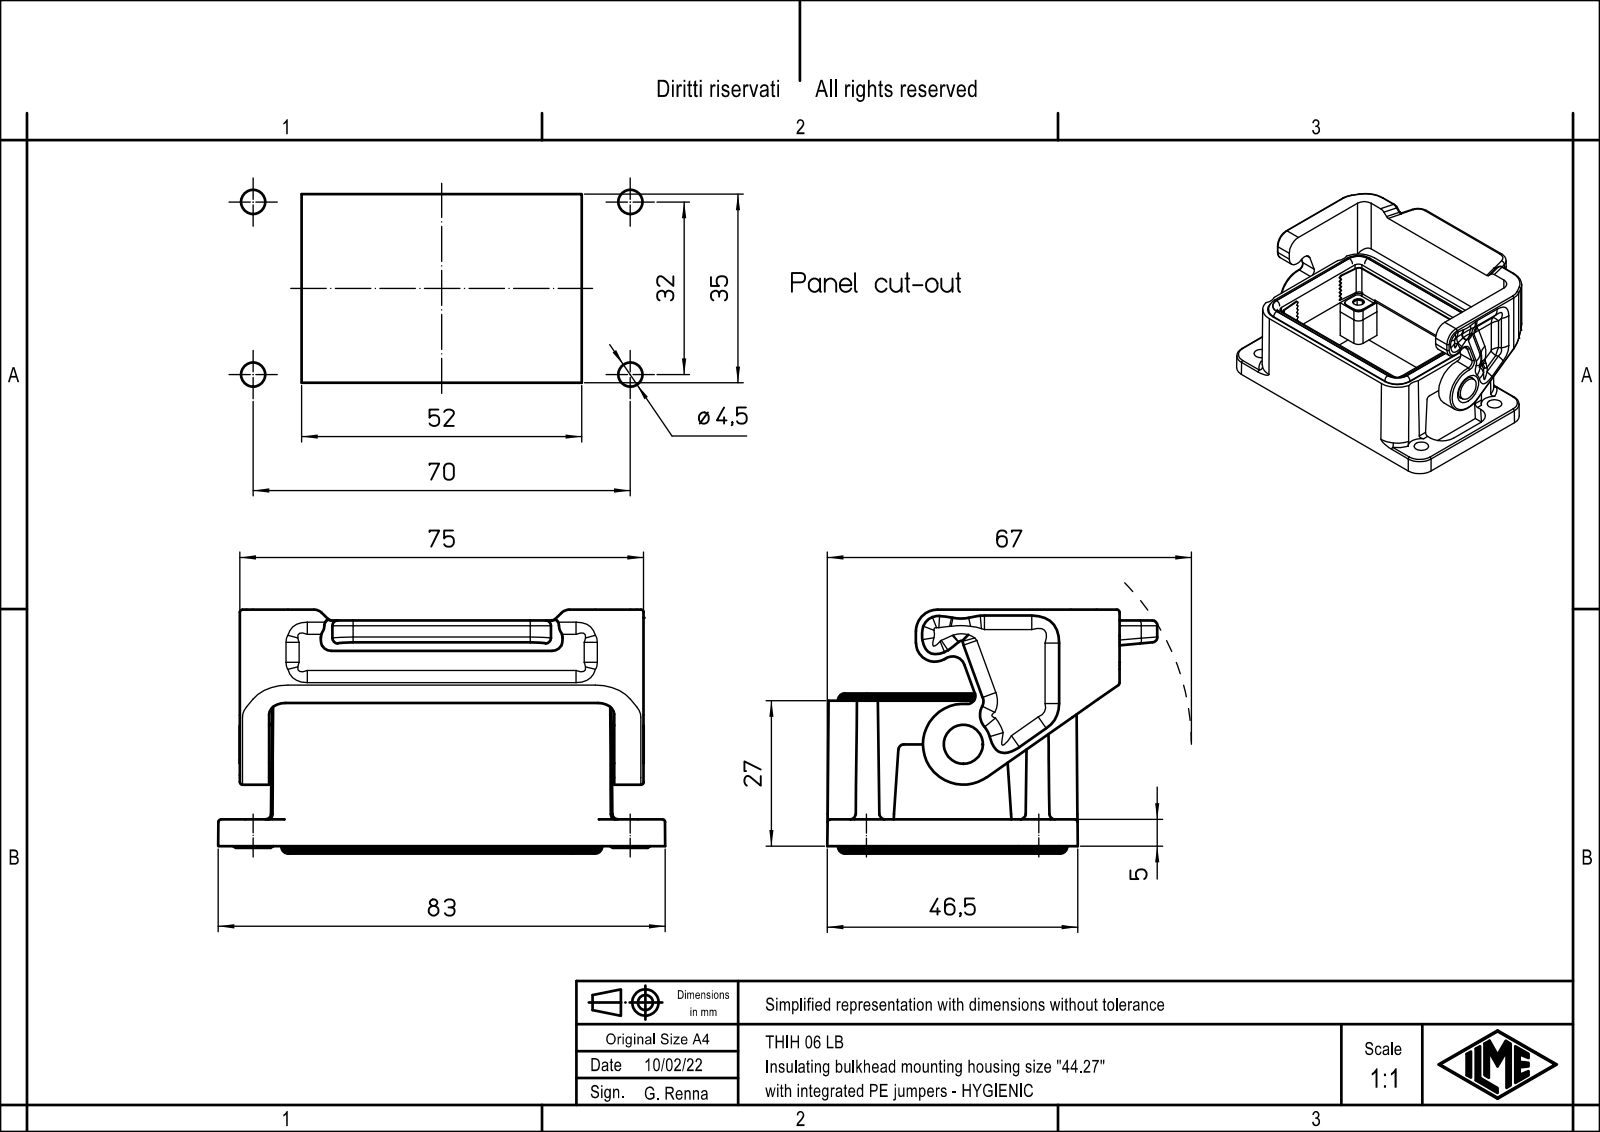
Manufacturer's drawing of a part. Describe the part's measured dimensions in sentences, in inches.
The part is named "53620_D; THIH_06_L". Its 3-D file was written by "Creo Elements/Direct Modeling 20.1B 02-Apr-2019 (C) Parametric Technology GmbH (AUTOMOTIVE_DESIGN)". It is 1 solid with 819 faces: 406 planar, 233 cylindrical and 180 other. Overall it measures 3.268 by 2.411 by 1.781 inches. Its volume is 2.952 cubic inches and its surface area 50.92 square inches. Round holes: 4 of diameter 0.098, 4 of diameter 0.138, 4 of diameter 0.177, 4 of diameter 0.272. Round bosses or shafts: 4 of diameter 0.189, 1 of diameter 0.276. Partial cylindrical surfaces (rounded edges, fillets, slot ends): 36 of radius 0.051, 24 of radius 0.039, 19 of radius 0.059, 15 of radius 0.079, 12 of radius 0.106, 12 of radius 0.217, 10 of radius 0.197, 7 of radius 0.118. The main face-to-face distances are 0.22, 2.265, 1.343, 1.512, 0.079, 0.217, 2.736, 0.197, 2.52, 0.169. The hole center spacings are 0.521, 1.269, 2.246, 2.527, 1.063, 1.26, 1.732, 2.032.
